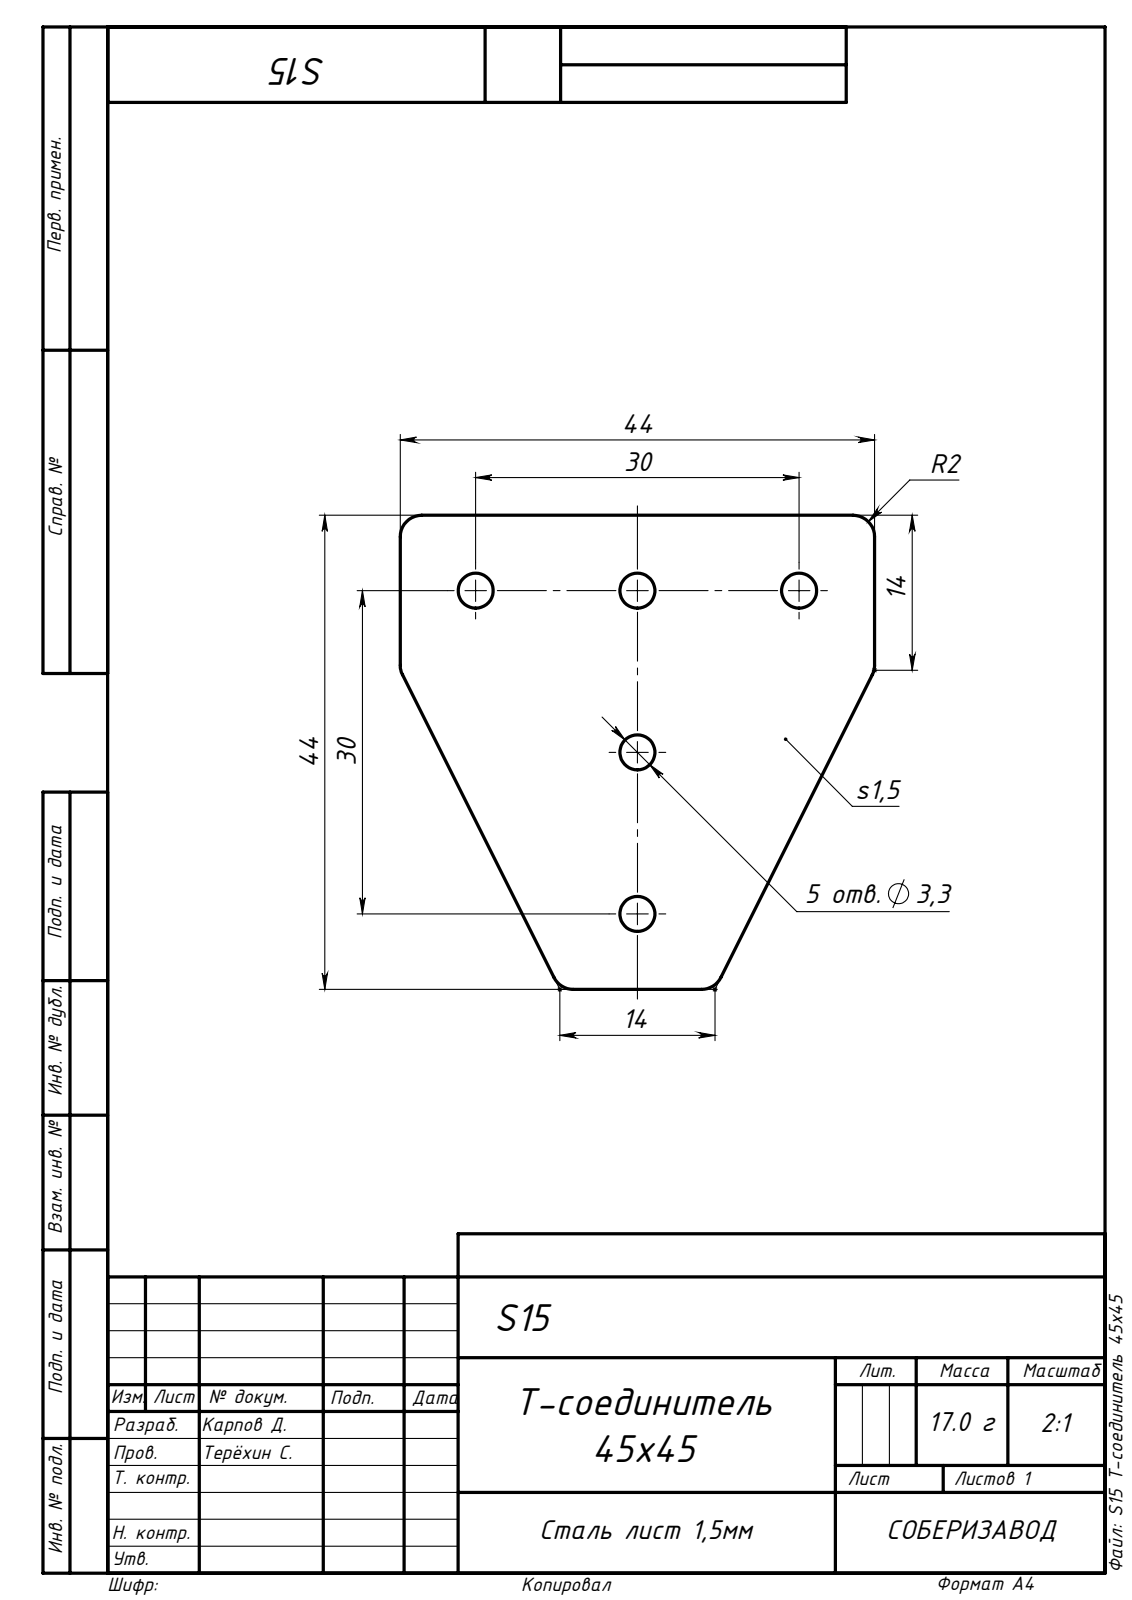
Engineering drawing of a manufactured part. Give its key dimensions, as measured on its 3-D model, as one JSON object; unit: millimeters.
{"part_name": "S15 Т-соединитель 45x45", "step_written_by": "SolidWorks 2019 (AUTOMOTIVE_DESIGN)", "units": "millimeters", "bodies": {"solids": 1, "faces": 24, "planar": 8, "cylindrical": 16, "other": 0}, "overall_size": [44, 44, 1.5], "volume_mm3": 2180, "surface_area_mm2": 3211, "round_holes": [[3.25, 5]], "partial_cylinders_radius": [[2, 6]], "face_to_face_distances": [1.5, 44], "hole_center_spacings": [15, 21.21, 30, 33.54]}
